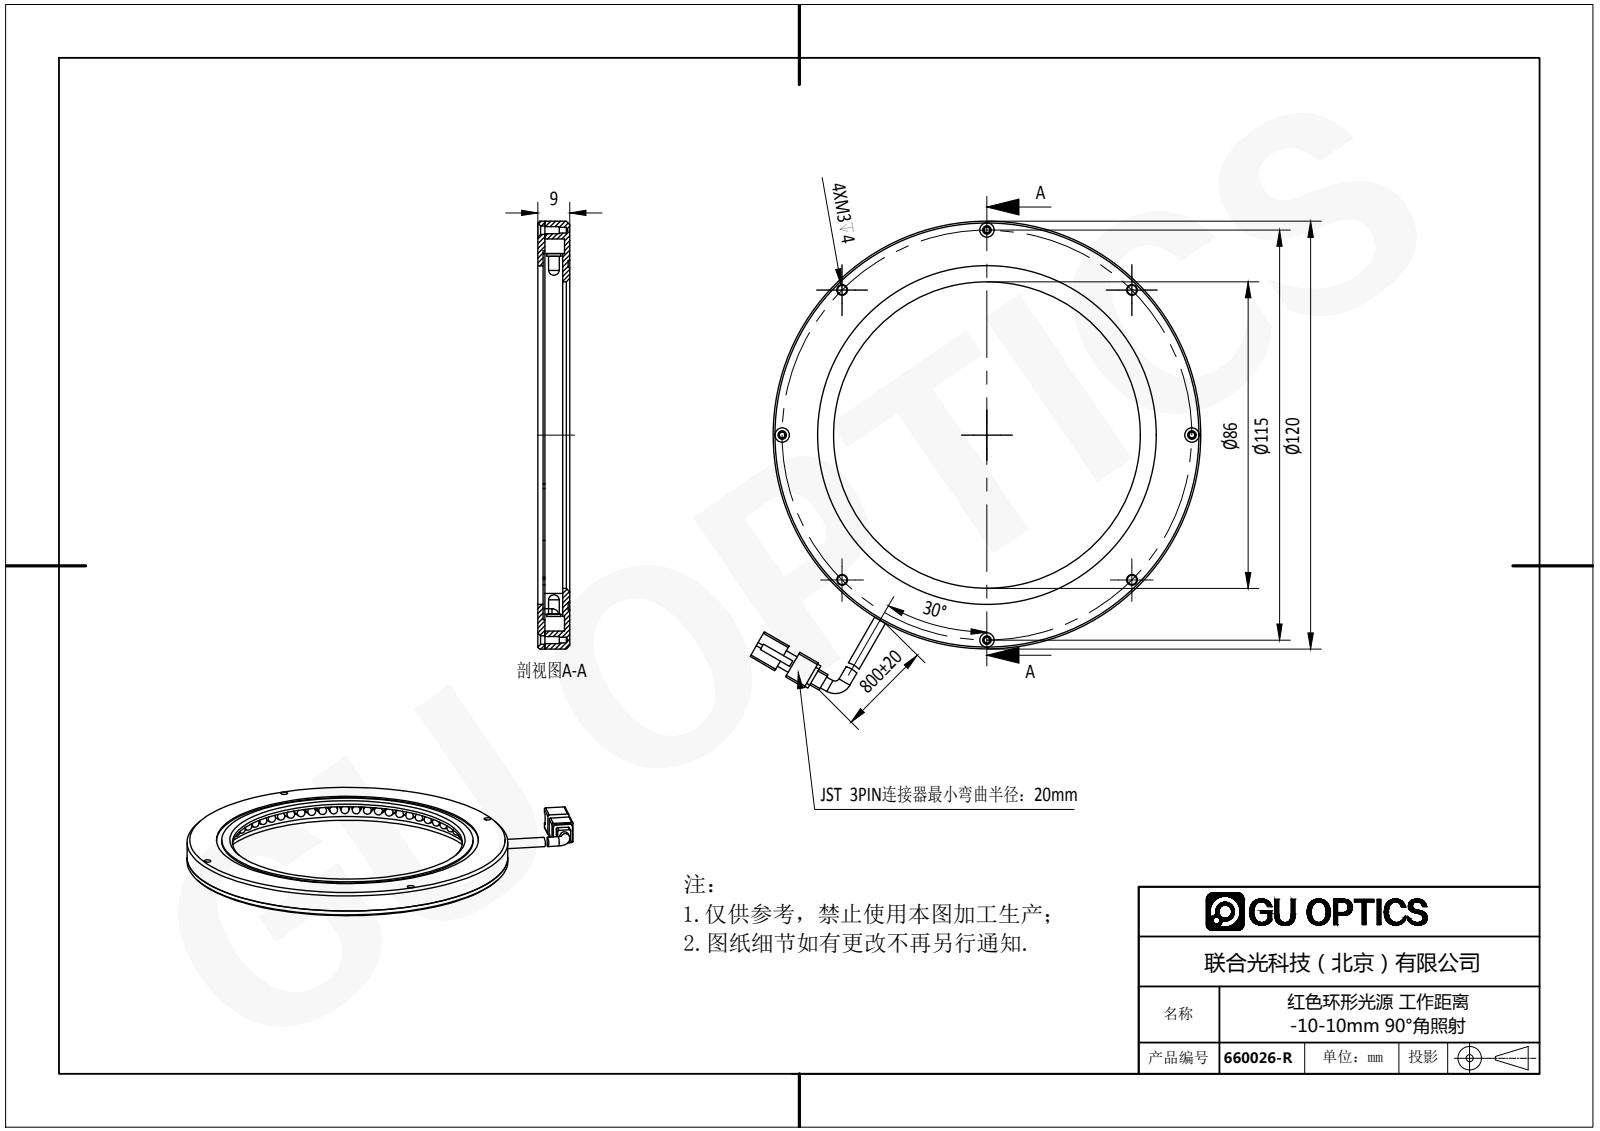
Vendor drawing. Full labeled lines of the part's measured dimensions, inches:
Part name (STEP PRODUCT): 660026-R
STEP written by: SolidWorks 2016 (AUTOMOTIVE_DESIGN)
Units: inches
Bodies: 75 solids, 1433 faces (928 planar, 409 cylindrical, 96 other)
Overall size (bounding box): 5.218 × 4.978 × 0.437
Volume: 1.874 in³ · Surface area: 59.39 in²
Round holes (diameter × count): ⌀0.063 ×4, ⌀0.079 ×4, ⌀0.094 ×4, ⌀0.102 ×4, ⌀0.118 ×4, ⌀0.138 ×1, ⌀3.386 ×1, ⌀3.74 ×1, ⌀3.858 ×1, ⌀4.055 ×1, ⌀4.075 ×1, ⌀4.331 ×1
Round bosses / shafts (diameter × count): ⌀0.15 ×69, ⌀0.118 ×69, ⌀0.138 ×2, ⌀4.724 ×1, ⌀4.079 ×1, ⌀4.008 ×1, ⌀3.701 ×1
Partial cylindrical surfaces — rounded edges, fillets, slot ends (radius × count): R0.039 ×12, R0.02 ×8, R0.081 ×2, R0.071 ×1, R0.295 ×1, R2.024 ×1, R2.126 ×1
Main face-to-face distances: 0.276, 0.079, 0.354, 0.02, 0.059, 0.217, 0.295, 0.197, 0.236, 0.039
Hole centre spacings: 1.733, 2.264, 3.202, 4.183, 4.183, 4.528, 1.732, 2.263
